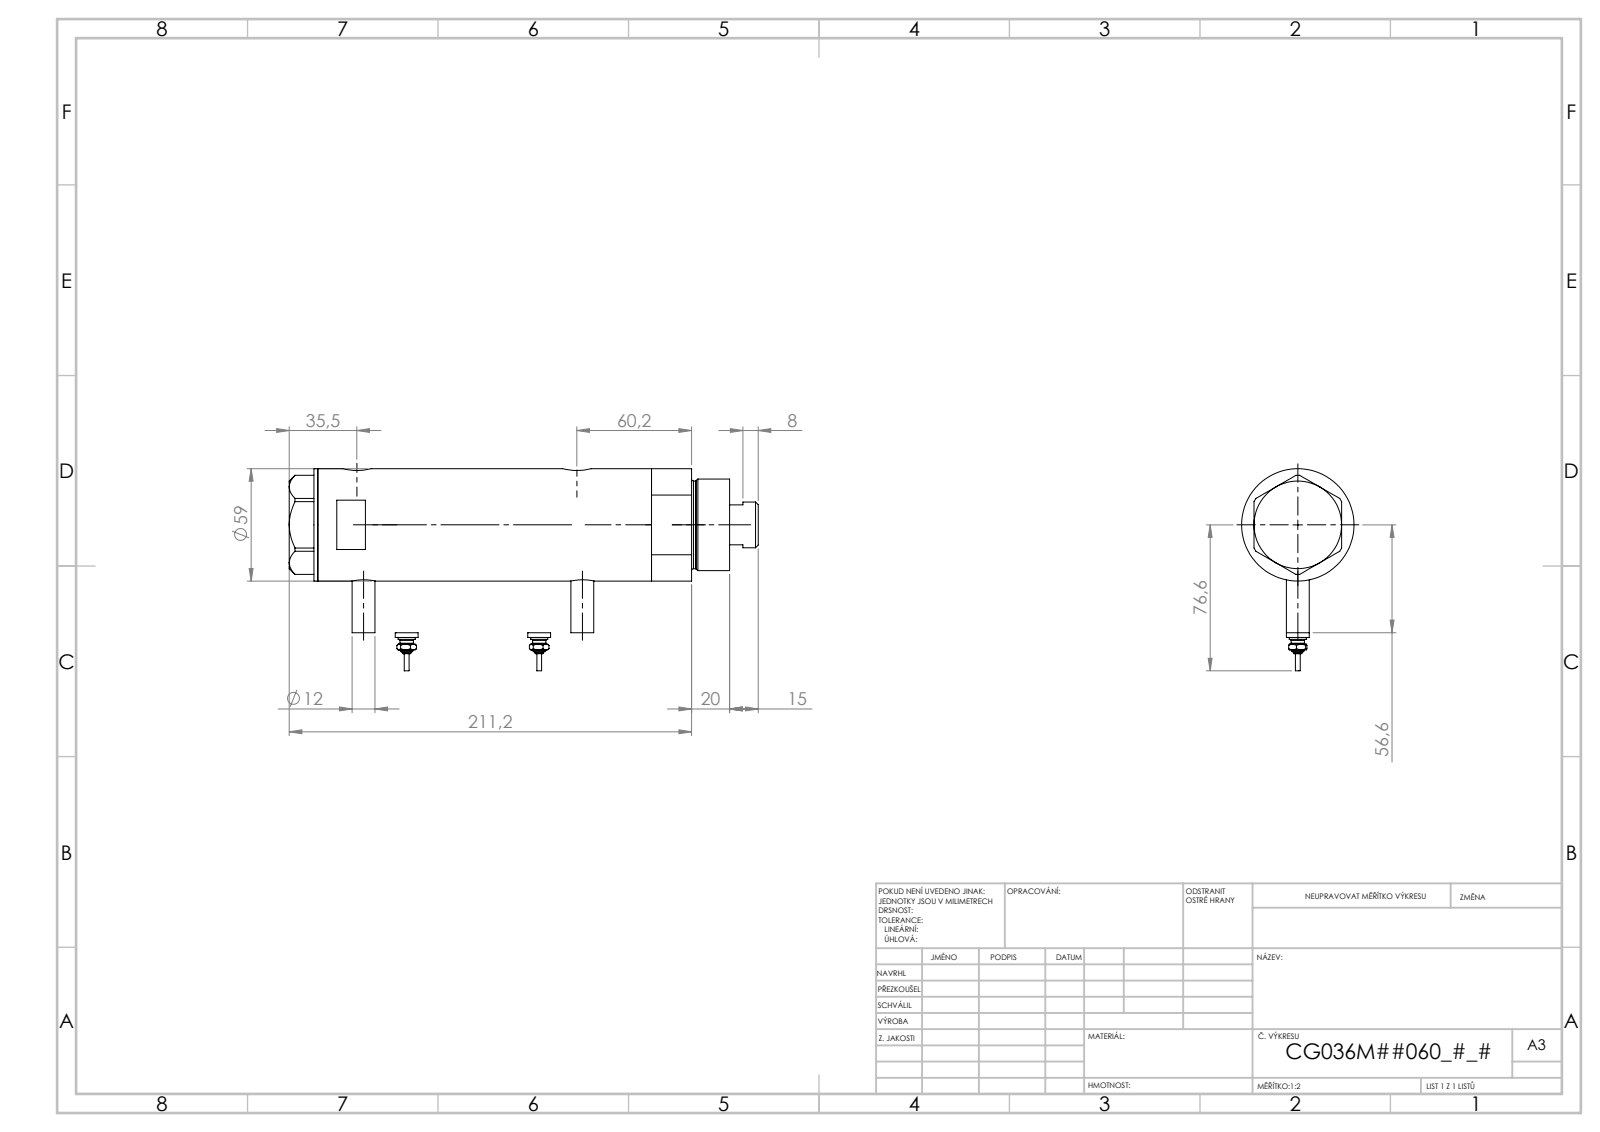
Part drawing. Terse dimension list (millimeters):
name: V270CG_SWITCH; V270CG_FRONT; V270CG_MIDDLE; V270CG_VC (+1 more)
written by: SolidWorks 2019 (CONFIG_CONTROL_DESIGN)
unit: mm
bodies: 6 solids, 232 faces (81 planar, 77 cylindrical, 74 other)
size: 223.42 × 91.3 × 59
volume: 506 416 mm³; area: 106 459 mm²
holes: 2× ⌀5, 2× ⌀9.73, 2× ⌀12.5, 2× ⌀15, 1× ⌀8.5, 1× ⌀25, 1× ⌀26.5, 1× ⌀36, 1× ⌀40, 1× ⌀52
bosses: 3× ⌀12, 2× ⌀9, 2× ⌀7, 2× ⌀4.34, 2× ⌀2.4, 1× ⌀59, 1× ⌀48, 1× ⌀46
face distances: 117.34, 23.5, 93.84, 15, 38.5, 132.34, 208.42, 193.42, 169.92, 76.08
hole spacings: 2.9, 3.5, 92.15, 95.05, 95.65, 98.55, 2.89, 2.91
